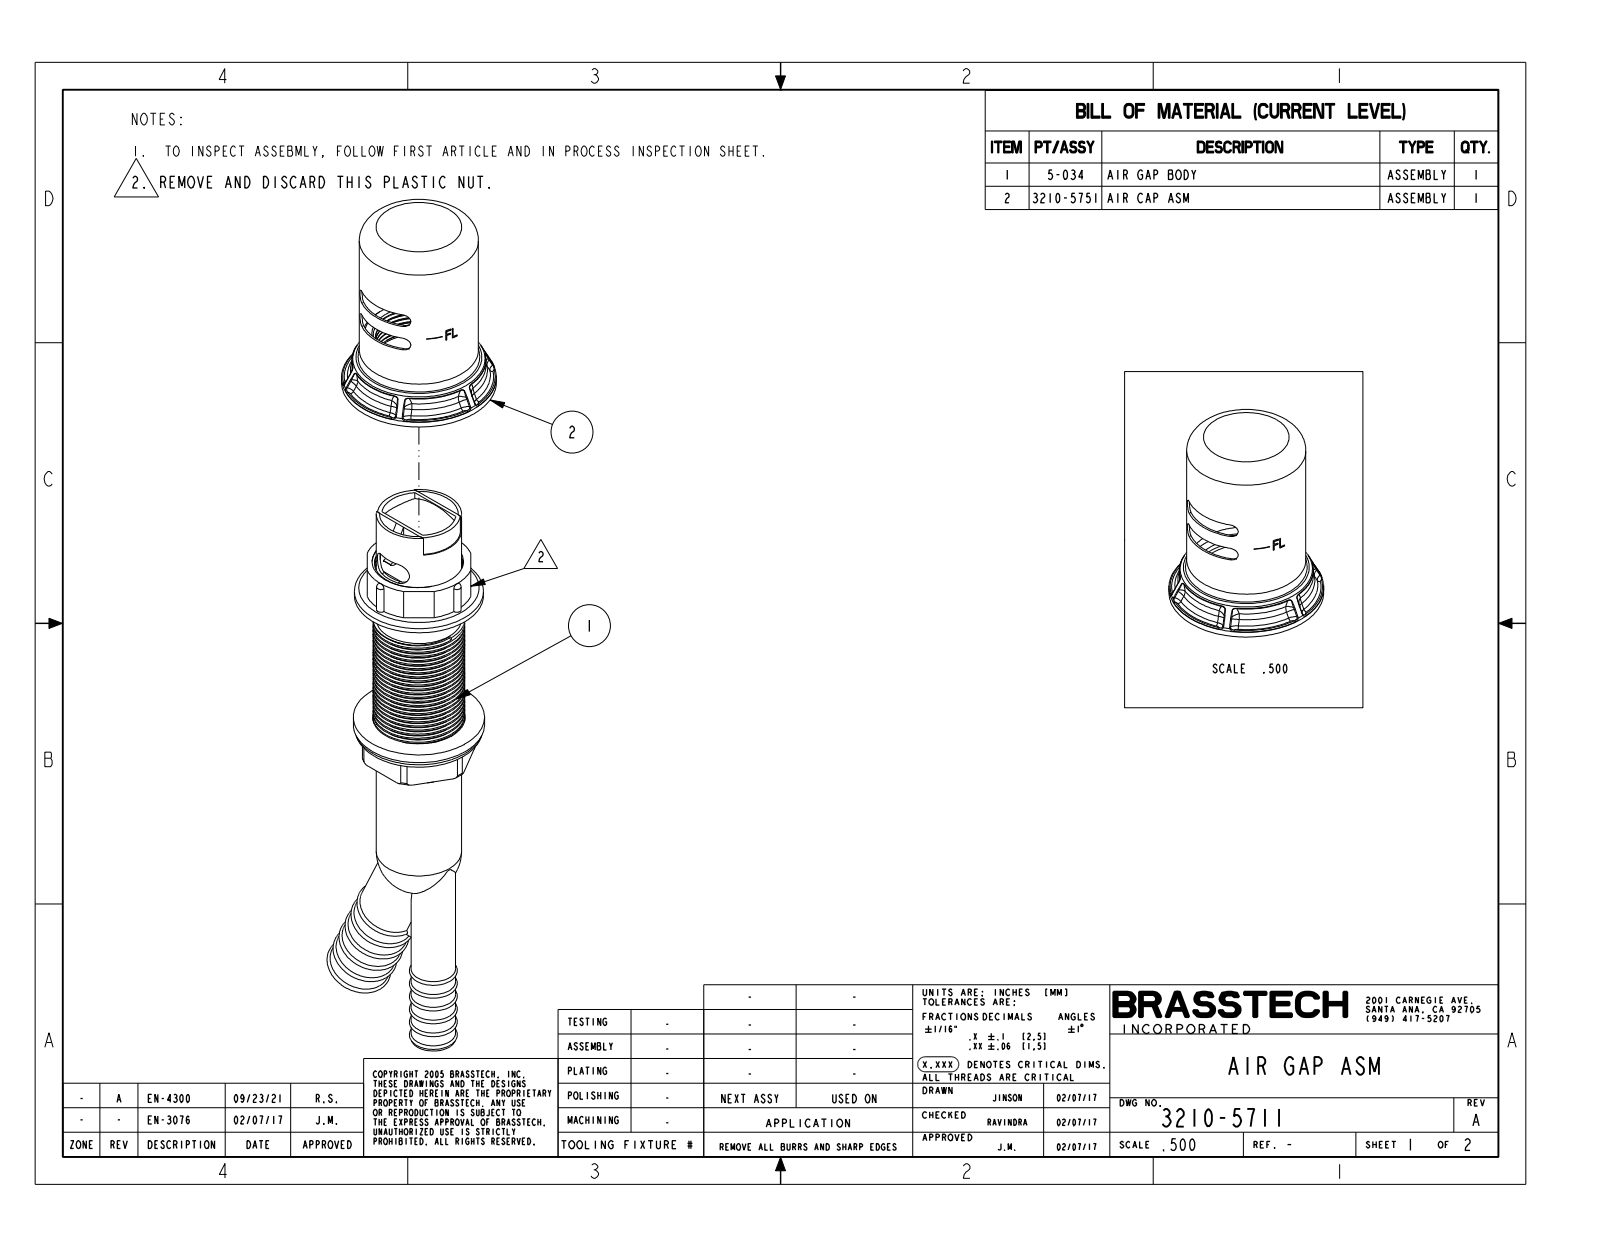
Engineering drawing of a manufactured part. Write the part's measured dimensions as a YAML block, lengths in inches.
part_name: "3210-5711"
step_written_by: "CREO PARAMETRIC BY PTC INC, 2018400 (AUTOMOTIVE_DESIGN)"
units: inches
bodies: {solids: 2, faces: 429, planar: 74, cylindrical: 138, other: 217}
overall_size: [8.803, 2.645, 2.125]
volume: 10.08
surface_area: 81.08
round_holes:
  - {diameter: 1.2, count: 1}
  - {diameter: 1.27, count: 1}
  - {diameter: 1.28, count: 1}
  - {diameter: 1.575, count: 1}
  - {diameter: 1.925, count: 1}
round_bosses_or_shafts:
  - {diameter: 2.125, count: 1}
  - {diameter: 1.8, count: 1}
  - {diameter: 1.76, count: 1}
  - {diameter: 1.685, count: 1}
  - {diameter: 1.635, count: 1}
  - {diameter: 1.259, count: 1}
  - {diameter: 1.17, count: 1}
  - {diameter: 0.854, count: 1}
partial_cylinders:
  - {radius: 0.04, count: 6}
  - {radius: 0.098, count: 4}
  - {radius: 0.157, count: 2}
  - {radius: 0.808, count: 1}
  - {radius: 0.92, count: 1}
face_to_face_distances: [0.92, 1.345, 0.425, 3.505, 3.535, 2.585, 2.615, 2.16, 2.19, 0.03]
